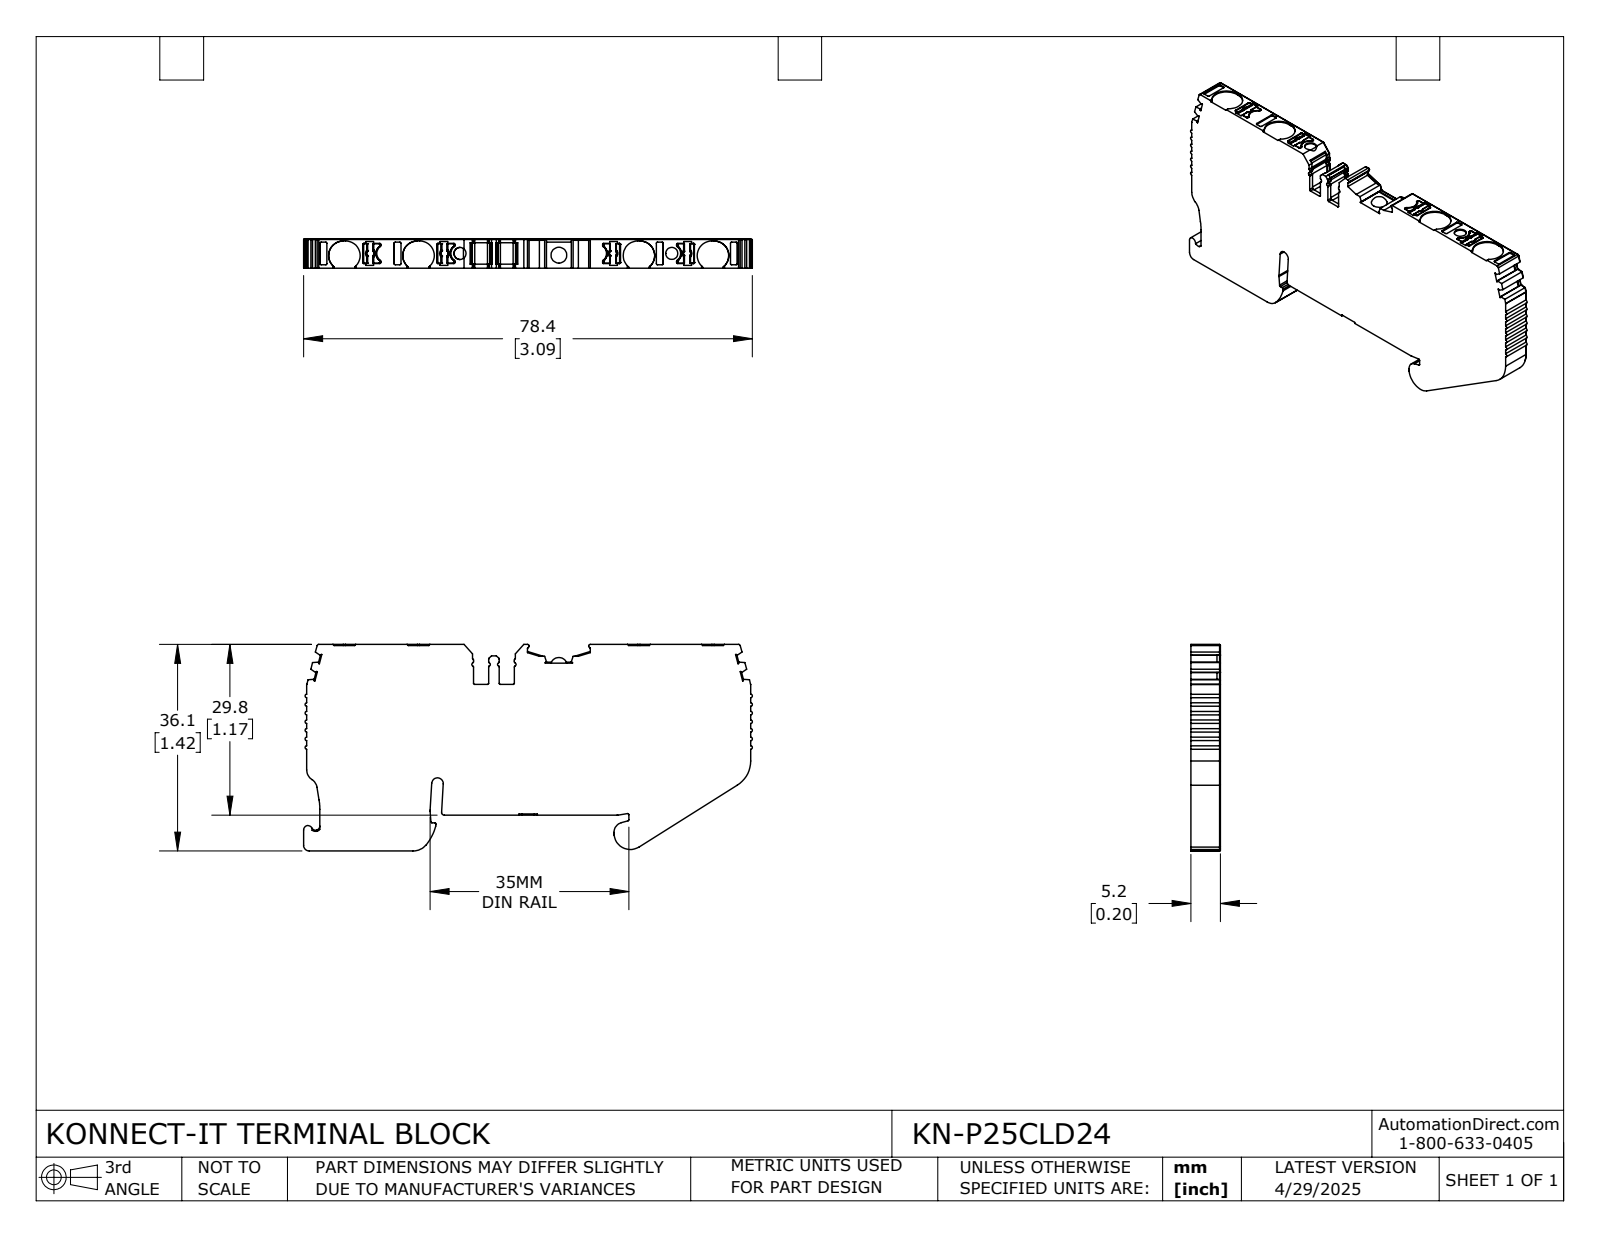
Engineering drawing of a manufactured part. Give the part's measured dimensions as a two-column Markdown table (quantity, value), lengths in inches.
| quantity | value |
| --- | --- |
| part name | KN-P25CLD24 |
| STEP written by | SolidWorks 2024 (CONFIG_CONTROL_DESIGN) |
| units | inches |
| bodies | 1 solid, 740 faces (381 planar, 291 cylindrical, 68 other) |
| overall size | 3.085 × 1.42 × 0.203 |
| volume | 0.731 in³ |
| surface area | 9.643 in² |
| round holes (diameter × count) | 0.083 × 2 |
| partial cylindrical surfaces (radius × count) | 0.008 × 78, 0.012 × 39, 0.004 × 21, 0.02 × 18, 0.006 × 16, 0.016 × 9, 0.1 × 8, 0.059 × 4 |
| main face-to-face distances | 0.203, 1.166, 1.174, 0.246, 1.412, 1.42, 3.052, 0.047, 0.197, 0.177 |
| hole center spacings | 1.456 |
